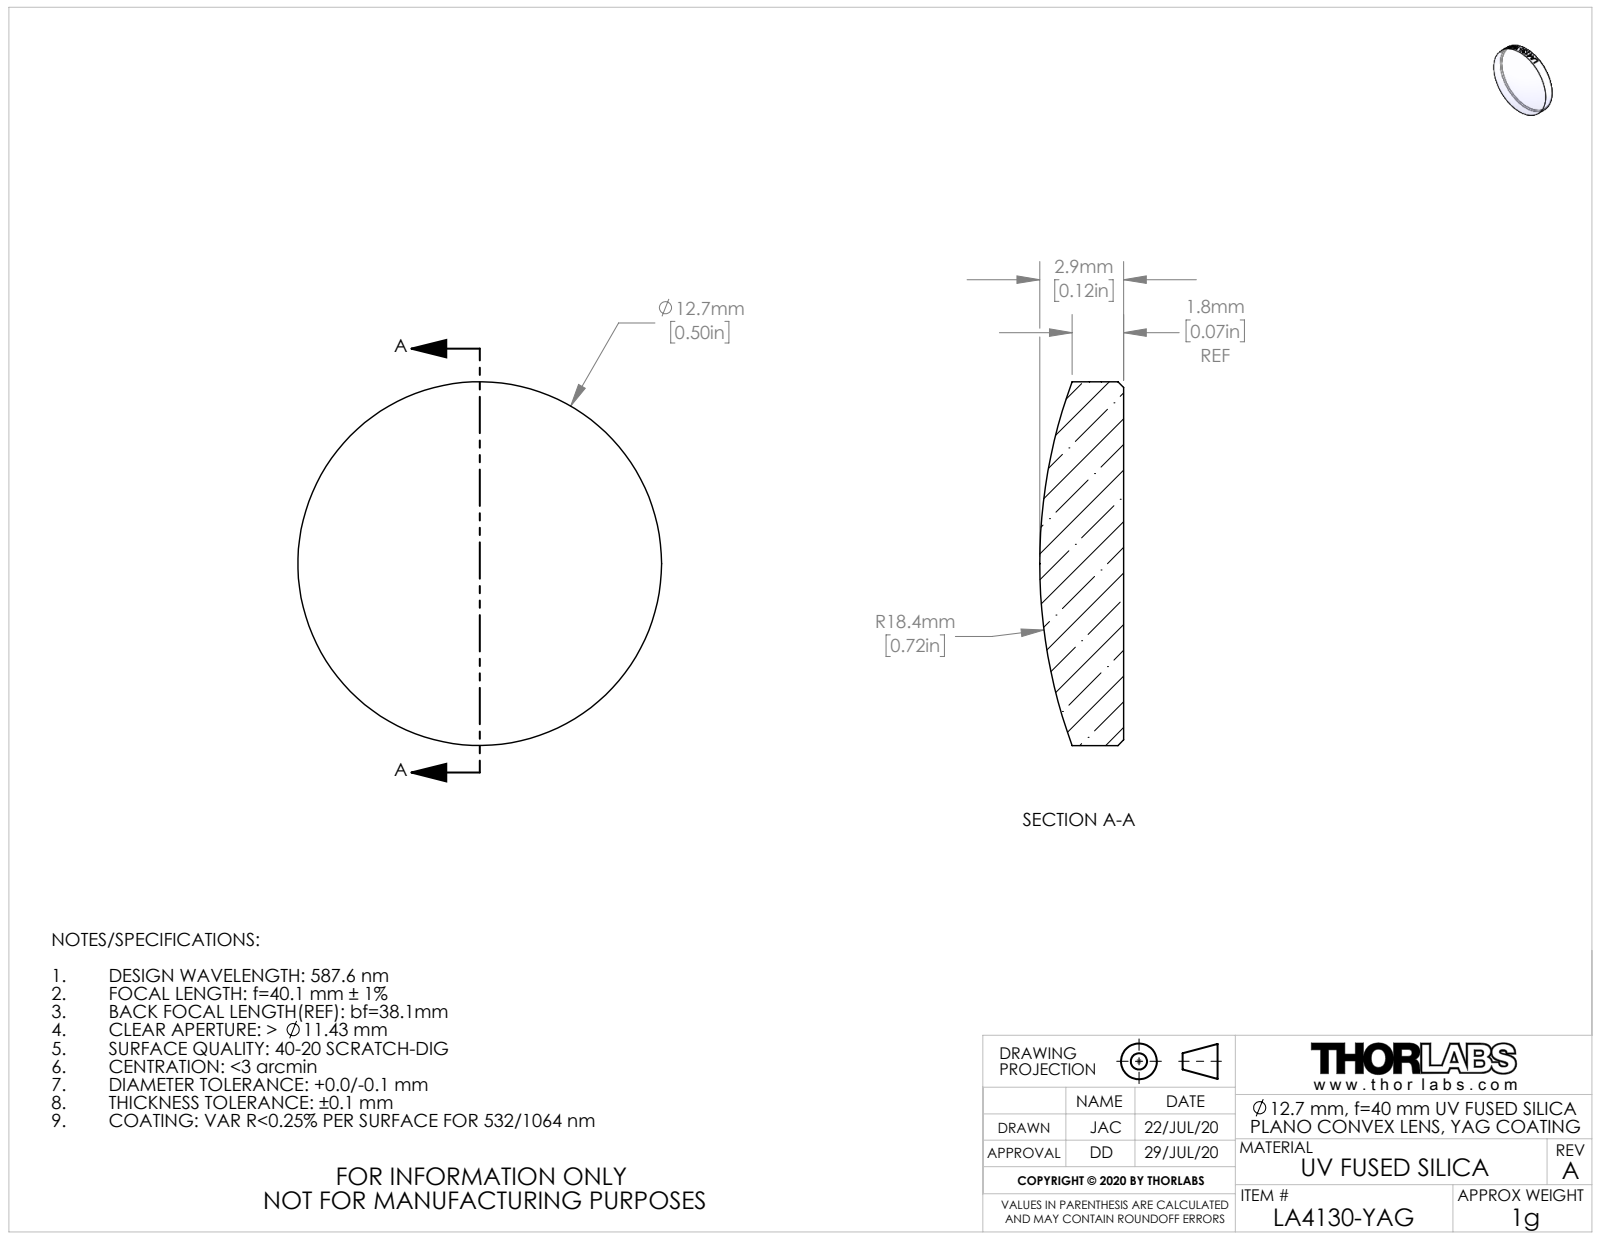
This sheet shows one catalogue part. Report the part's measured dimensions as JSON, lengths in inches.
{"part_name": "TTN217848-E0W", "step_written_by": "SolidWorks 2018 (CONFIG_CONTROL_DESIGN)", "units": "inches", "bodies": {"solids": 1, "faces": 25, "planar": 1, "cylindrical": 20, "other": 4}, "overall_size": [0.5, 0.5, 0.115], "volume_in3": 0.018, "surface_area_in2": 0.503, "round_bosses_or_shafts": [[0.5, 1]]}
